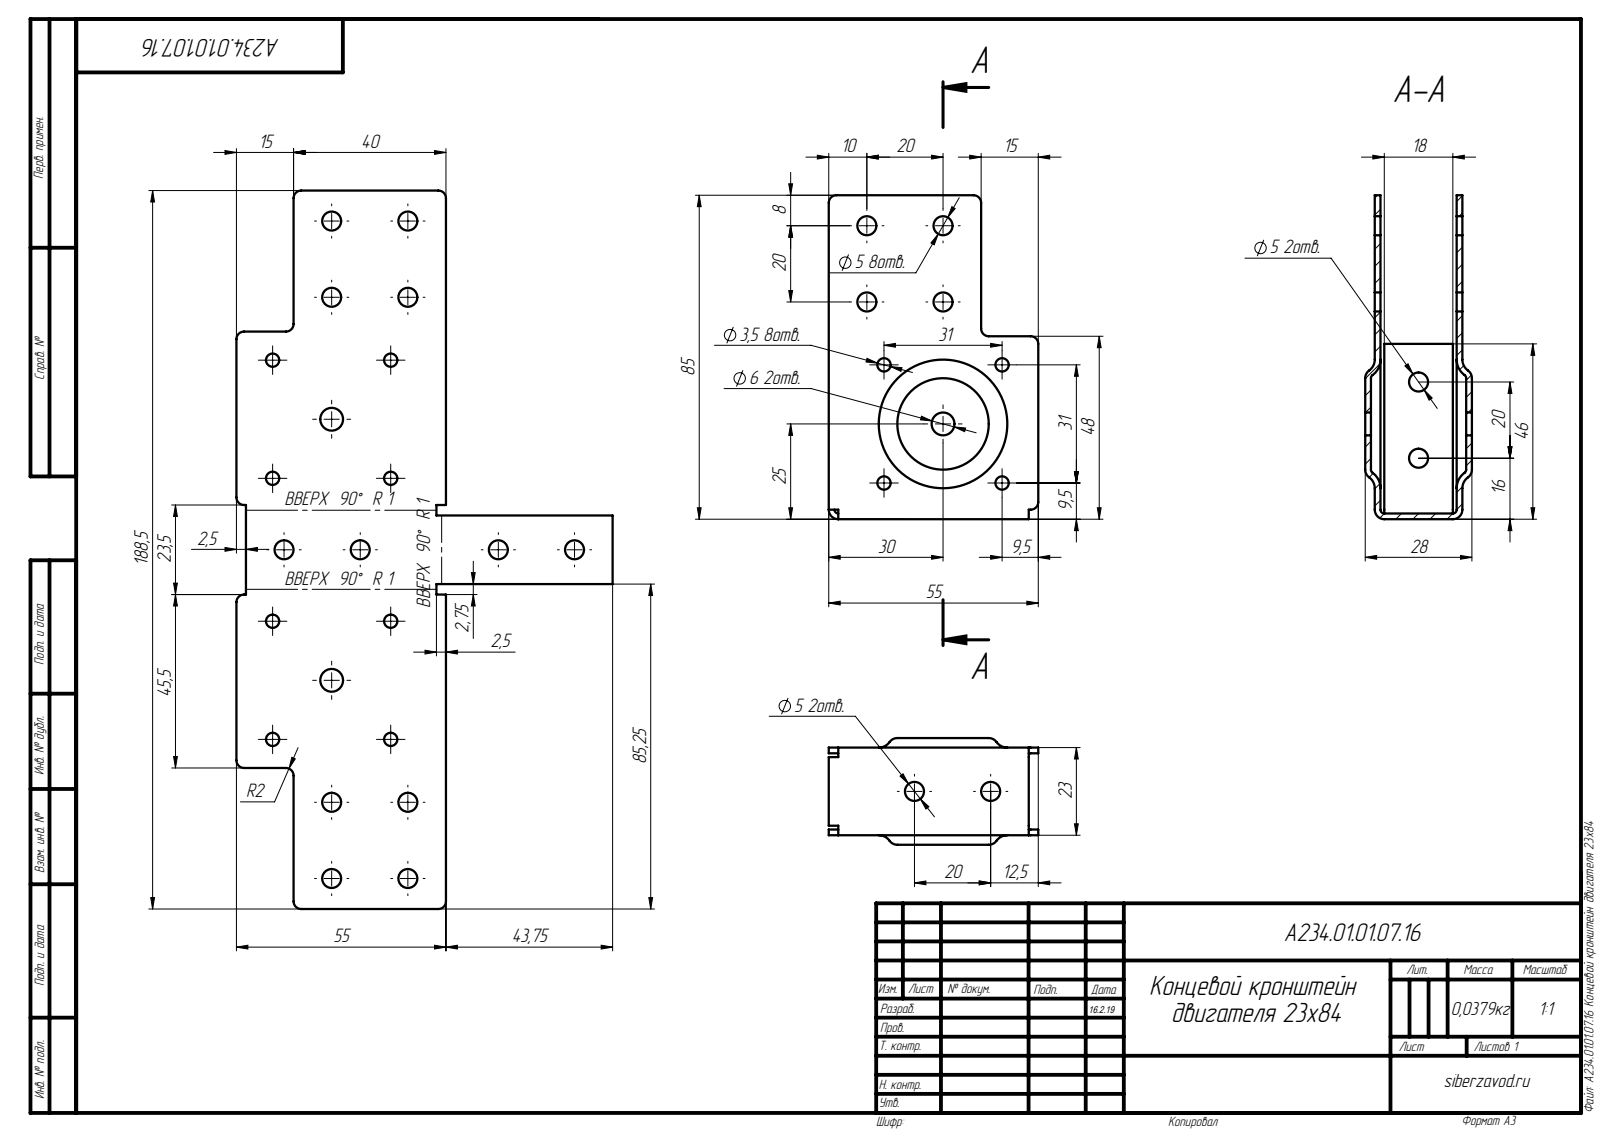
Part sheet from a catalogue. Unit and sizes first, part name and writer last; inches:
Units: inches
Overall size (bounding box): 3.346 × 2.165 × 1.102
Round holes (diameter × count): ⌀0.197 ×8, ⌀0.138 ×4, ⌀0.236 ×1
Partial cylindrical surfaces — rounded edges, fillets, slot ends (radius × count): R0.079 ×5, R0.039 ×3, R0.098 ×3
Main face-to-face distances: 0.059, 0.846, 0.906, 0.787, 0.098, 0.945, 0.039, 0.157, 1.004, 1.043
Hole centre spacings: 0.787, 0.863, 1.22, 0.891, 1.113, 1.561, 1.726, 1.967
Volume: 0.892 in³ · Surface area: 32.27 in²
Bodies: 1 solid, 110 faces (34 planar, 60 cylindrical, 16 other)
Part name (STEP PRODUCT): A163 Концевой кронштейн двигателя 23х84
STEP written by: SolidWorks 2018 (AUTOMOTIVE_DESIGN)
